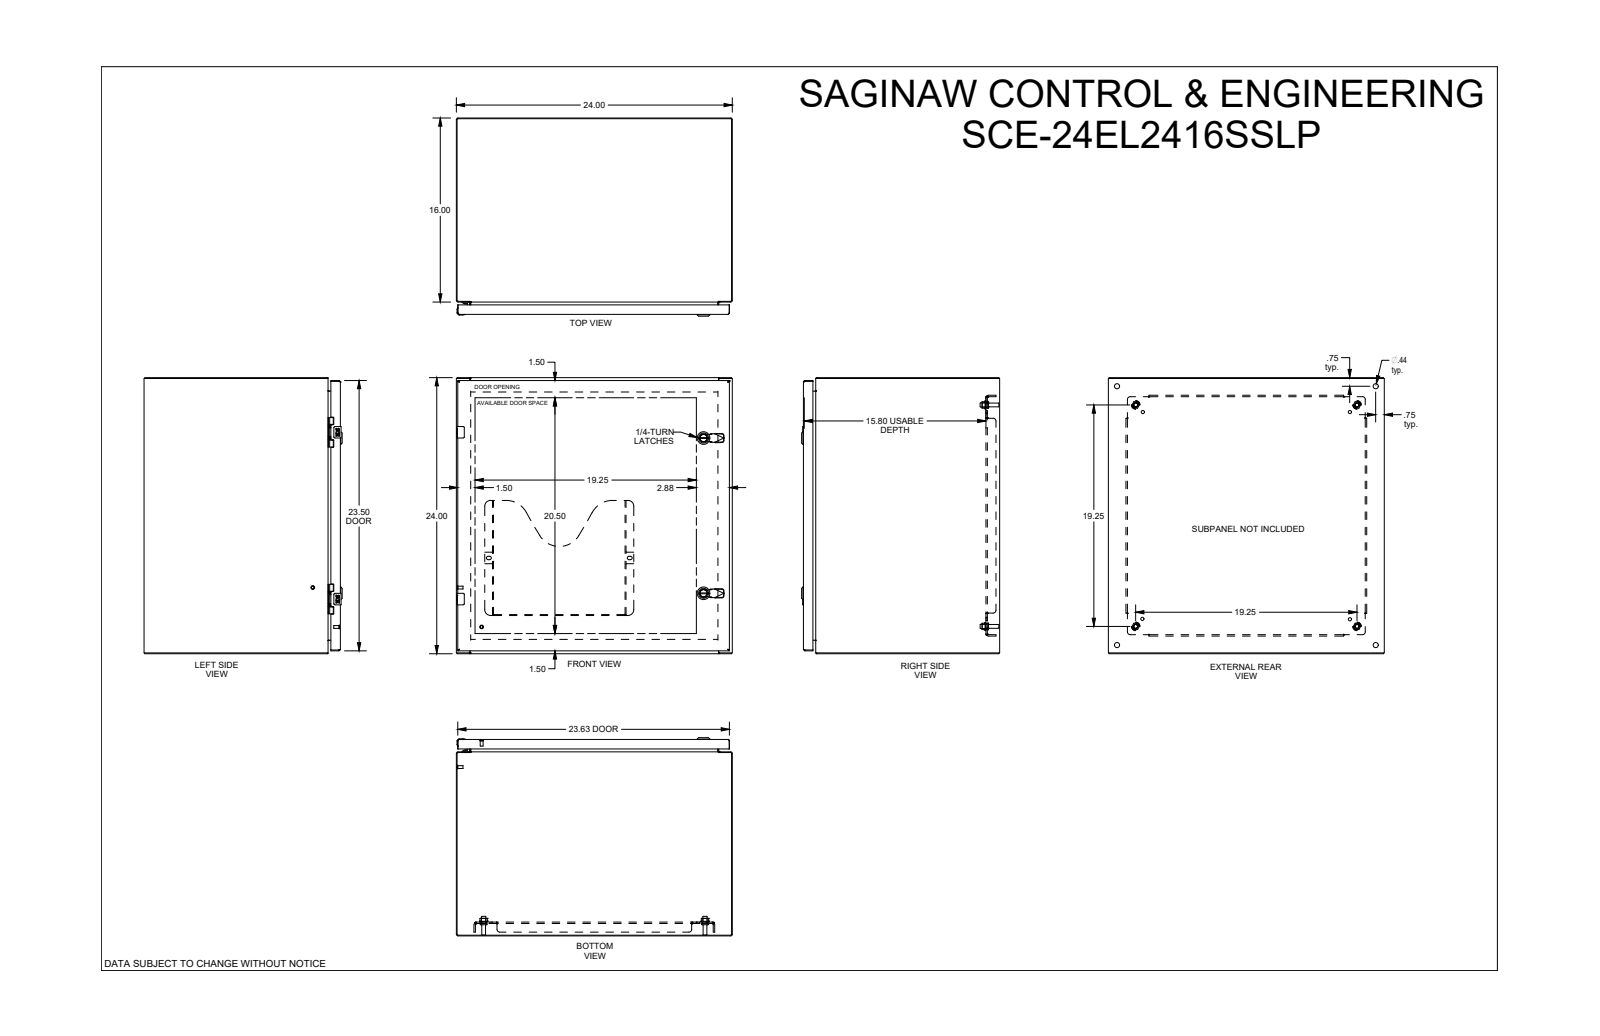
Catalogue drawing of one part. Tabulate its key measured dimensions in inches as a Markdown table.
| quantity | value |
| --- | --- |
| part name | SCE-24EL2416SSLP |
| STEP written by | SolidWorks 2019 (CONFIG_CONTROL_DESIGN) |
| units | inches |
| bodies | 0 solids, 2838 faces (1307 planar, 759 cylindrical, 772 other) |
| overall size | 24 × 24 × 17.23 |
| round holes (diameter × count) | 0.172 × 4, 0.205 × 4, 0.244 × 4, 0.266 × 4, 0.281 × 4, 0.367 × 4, 0.375 × 4, 0.437 × 4, 0.5 × 4, 0.156 × 2, 0.197 × 2, 0.218 × 2 |
| round bosses / shafts (diameter × count) | 0.17 × 6, 0.366 × 4, 0.332 × 4, 0.25 × 4, 0.248 × 4, 0.196 × 3, 1.102 × 2, 0.866 × 2 |
| partial cylindrical surfaces (radius × count) | 0.012 × 56, 0.015 × 32, 0.01 × 28, 0.04 × 23, 0.02 × 20, 0.029 × 12, 0.07 × 10, 0.145 × 10 |
| main face-to-face distances | 0.075, 23.925, 23.85, 24, 0.075, 16.998, 16.923, 17.073, 16.998, 1.2 |
| hole center spacings | 14.5, 20.938, 0.985, 18.641, 20.38, 0.02, 0.875, 2.298 |
